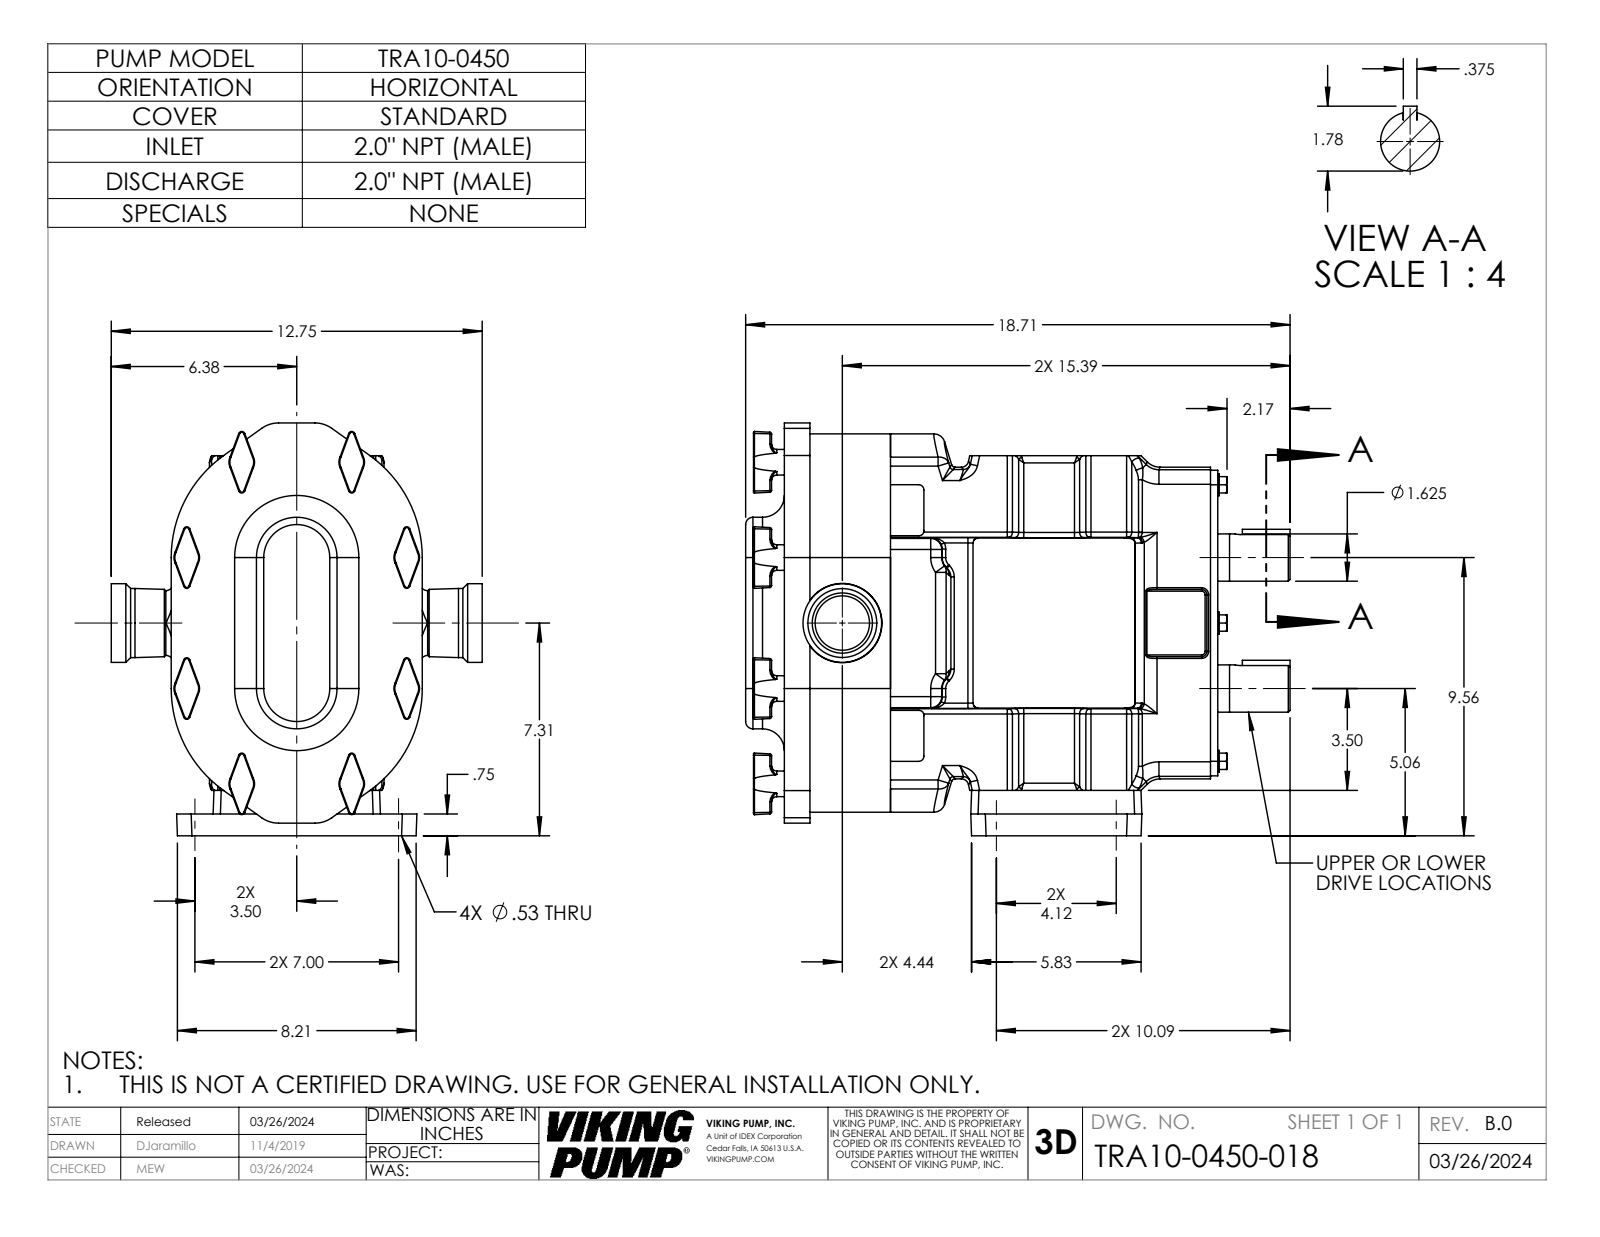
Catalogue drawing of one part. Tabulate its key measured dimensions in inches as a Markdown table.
| quantity | value |
| --- | --- |
| part name | 0600NPT20; TRA10-0600-GEARBOX-H; TRA10-0450-BODY; TRA10-0600-COVER-STD (+1 more) |
| STEP written by | SolidWorks 2022 (AUTOMOTIVE_DESIGN) |
| units | inches |
| bodies | 5 solids, 1044 faces (281 planar, 371 cylindrical, 392 other) |
| overall size | 18.714 × 14.185 × 12.75 |
| volume | 1 186 in³ |
| surface area | 1 356 in² |
| round holes (diameter × count) | 0.531 × 4, 1.87 × 1, 2.07 × 1, 2.368 × 1 |
| round bosses / shafts (diameter × count) | 0.88 × 8, 0.75 × 6, 1.624 × 2, 2.704 × 1, 2.375 × 1 |
| partial cylindrical surfaces (radius × count) | 0.18 × 44, 0.06 × 43, 0.03 × 32, 0.25 × 32, 0.38 × 28, 0.12 × 24, 0.5 × 20, 0.375 × 12 |
| main face-to-face distances | 2.769, 0.5, 0.88, 3.649, 0.36, 14.899, 14.019, 11.25, 6.5, 0.86 |
| hole center spacings | 4.12, 7, 8.122 |
